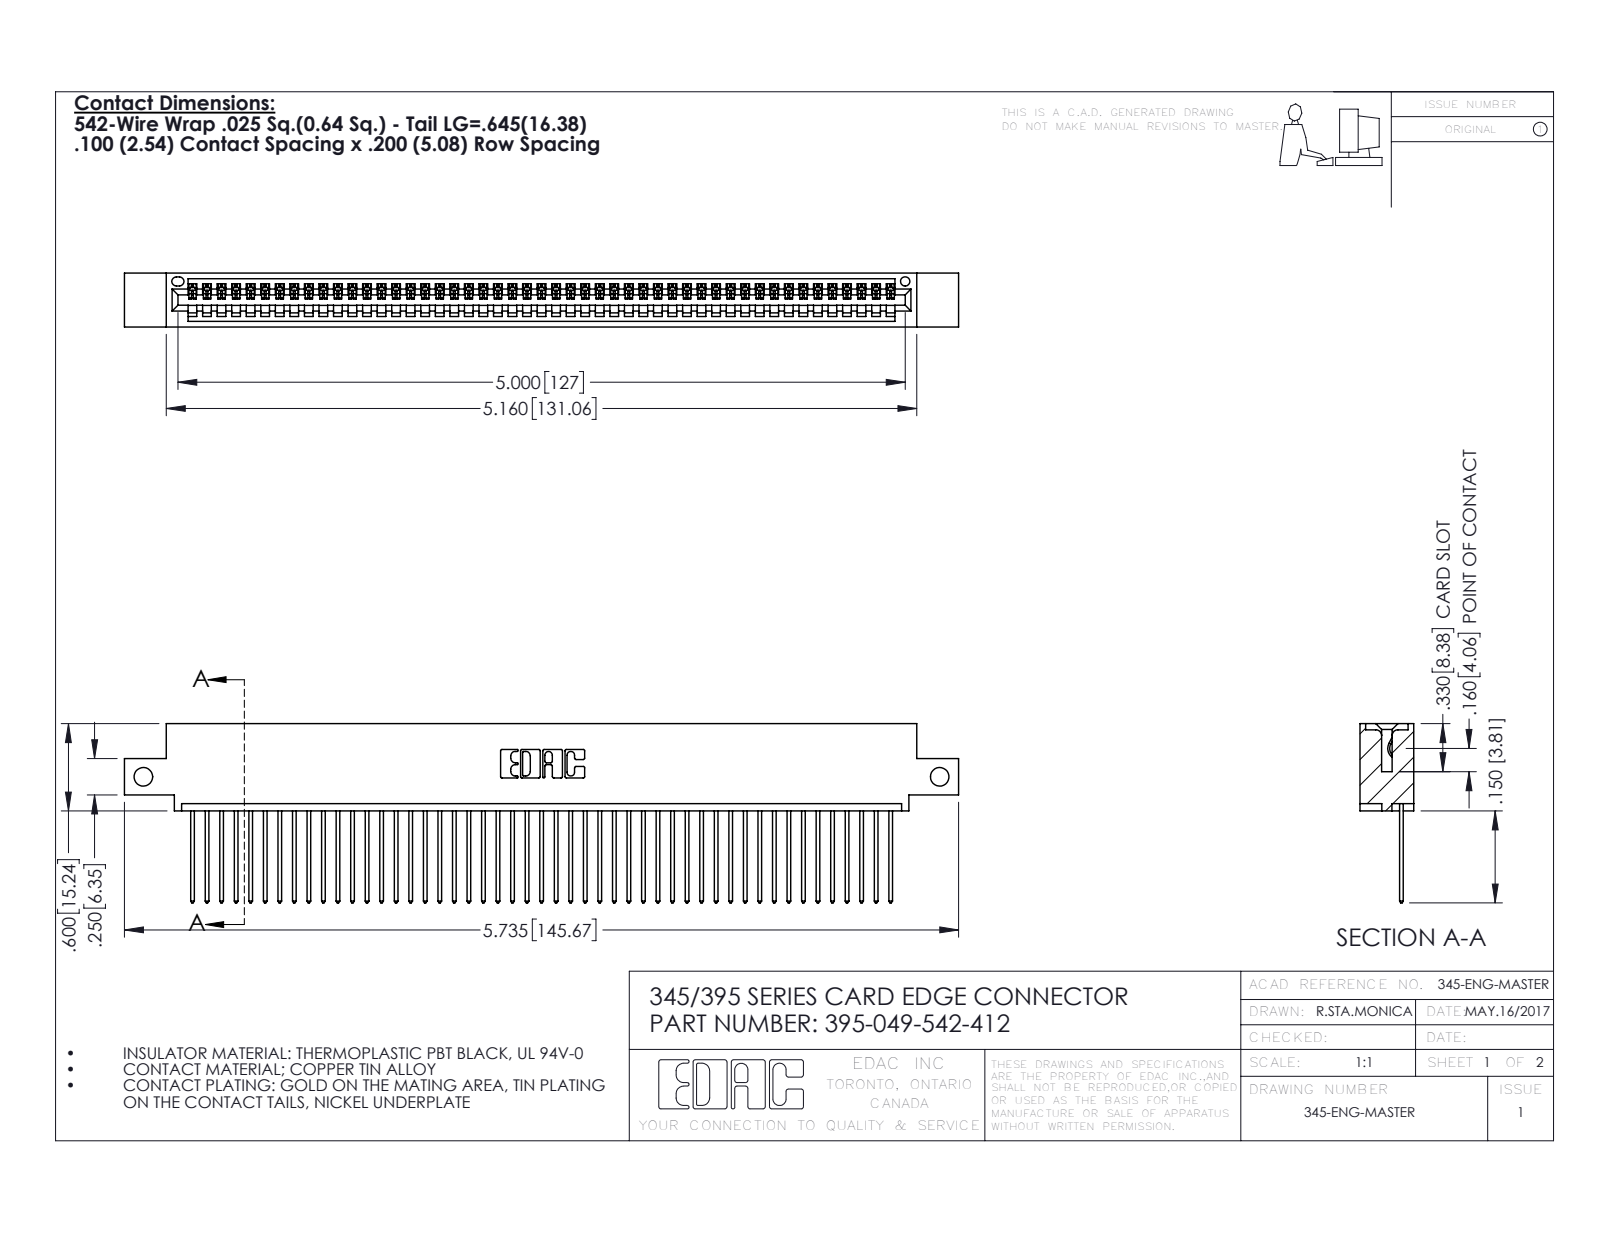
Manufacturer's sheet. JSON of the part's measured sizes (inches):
{"part_name": "345 Part_0.110 Offset - Side Mount; 345-292-001_345-293-142; 395-049-542-412", "step_written_by": "SolidWorks 2016 (CONFIG_CONTROL_DESIGN)", "units": "inches", "bodies": {"solids": 50, "faces": 2972, "planar": 2044, "cylindrical": 928, "other": 0}, "overall_size": [5.735, 1.232, 0.37], "volume_in3": 0.845, "surface_area_in2": 29.63, "round_holes": [[0.128, 2], [0.064, 1]], "partial_cylinders_radius": [[0.006, 98], [0.01, 98], [0.01, 22], [0.007, 6], [0.031, 6], [0.026, 3], [0.031, 2], [0.04, 2]], "face_to_face_distances": [0.072, 0.298, 0.098, 0.272, 0.025, 0.37, 0.2, 0.225, 0.149, 0.072], "hole_center_spacings": [5.475]}
